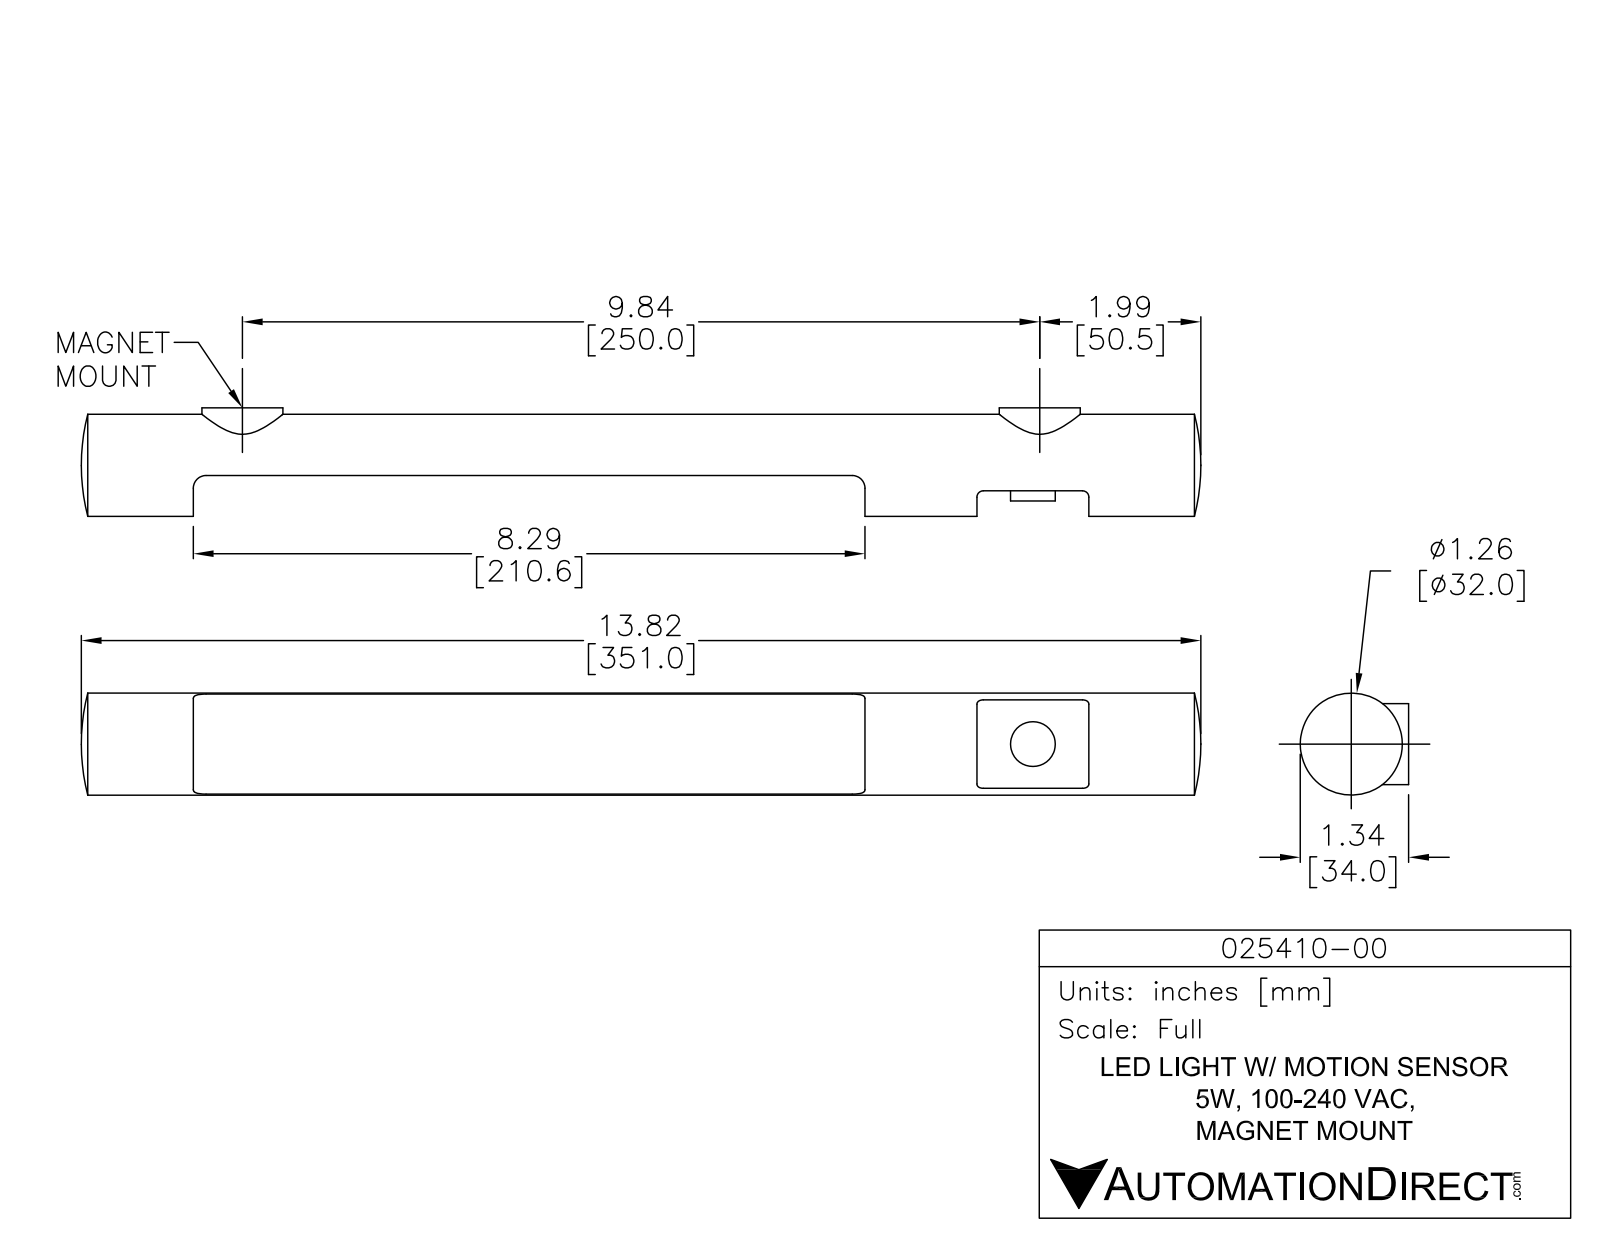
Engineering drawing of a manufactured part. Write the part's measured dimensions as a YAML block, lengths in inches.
part_name: "025410-00"
step_written_by: "SolidWorks 2013 (AUTOMOTIVE_DESIGN)"
units: inches
bodies: {solids: 1, faces: 129, planar: 76, cylindrical: 33, other: 20}
overall_size: [13.758, 1.515, 1.26]
volume: 13.46
surface_area: 58.18
round_holes:
  - {diameter: 0.077, count: 2}
  - {diameter: 0.892, count: 1}
round_bosses_or_shafts:
  - {diameter: 0.985, count: 2}
  - {diameter: 0.073, count: 2}
  - {diameter: 1.26, count: 1}
  - {diameter: 0.865, count: 1}
  - {diameter: 0.865, count: 1}
partial_cylinders:
  - {radius: 0.06, count: 4}
  - {radius: 0.12, count: 2}
  - {radius: 0.2, count: 2}
  - {radius: 0.4, count: 2}
face_to_face_distances: [0.885, 0.03, 0.325, 0.04, 0.845, 0.53, 0.03, 0.545, 0.49, 0.355]
hole_center_spacings: [0.2]
